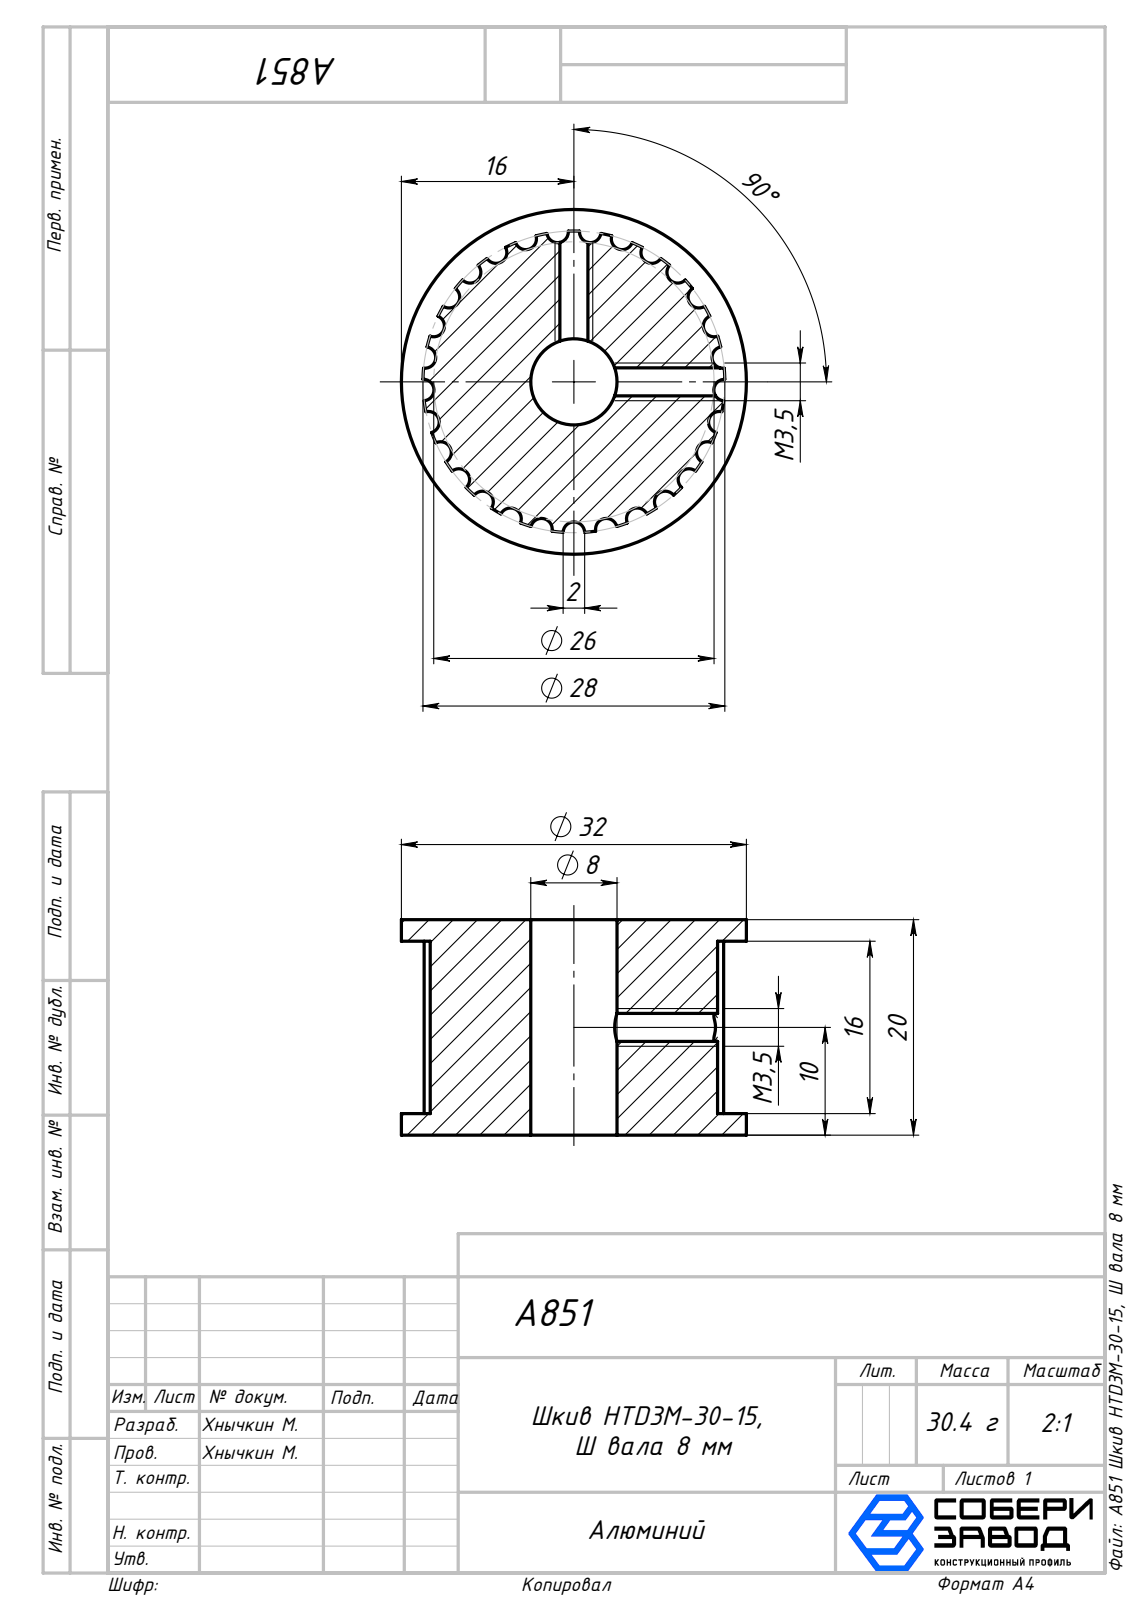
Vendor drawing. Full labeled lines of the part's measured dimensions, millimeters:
Part name (STEP PRODUCT): A851 Шкив HTD3M-30-15, Ø вала 8 мм
STEP written by: SolidWorks 2025 (AUTOMOTIVE_DESIGN)
Units: millimetres
Bodies: 1 solid, 90 faces (4 planar, 86 cylindrical, 0 other)
Overall size (bounding box): 32 × 32 × 20
Volume: 11 244 mm³ · Surface area: 4 913 mm²
Round holes (diameter × count): ⌀2.6 ×2, ⌀8 ×1
Round bosses / shafts (diameter × count): ⌀32 ×1
Partial cylindrical surfaces — rounded edges, fillets, slot ends (radius × count): R1 ×29, R14 ×1
Main face-to-face distances: 20, 2, 18, 16
